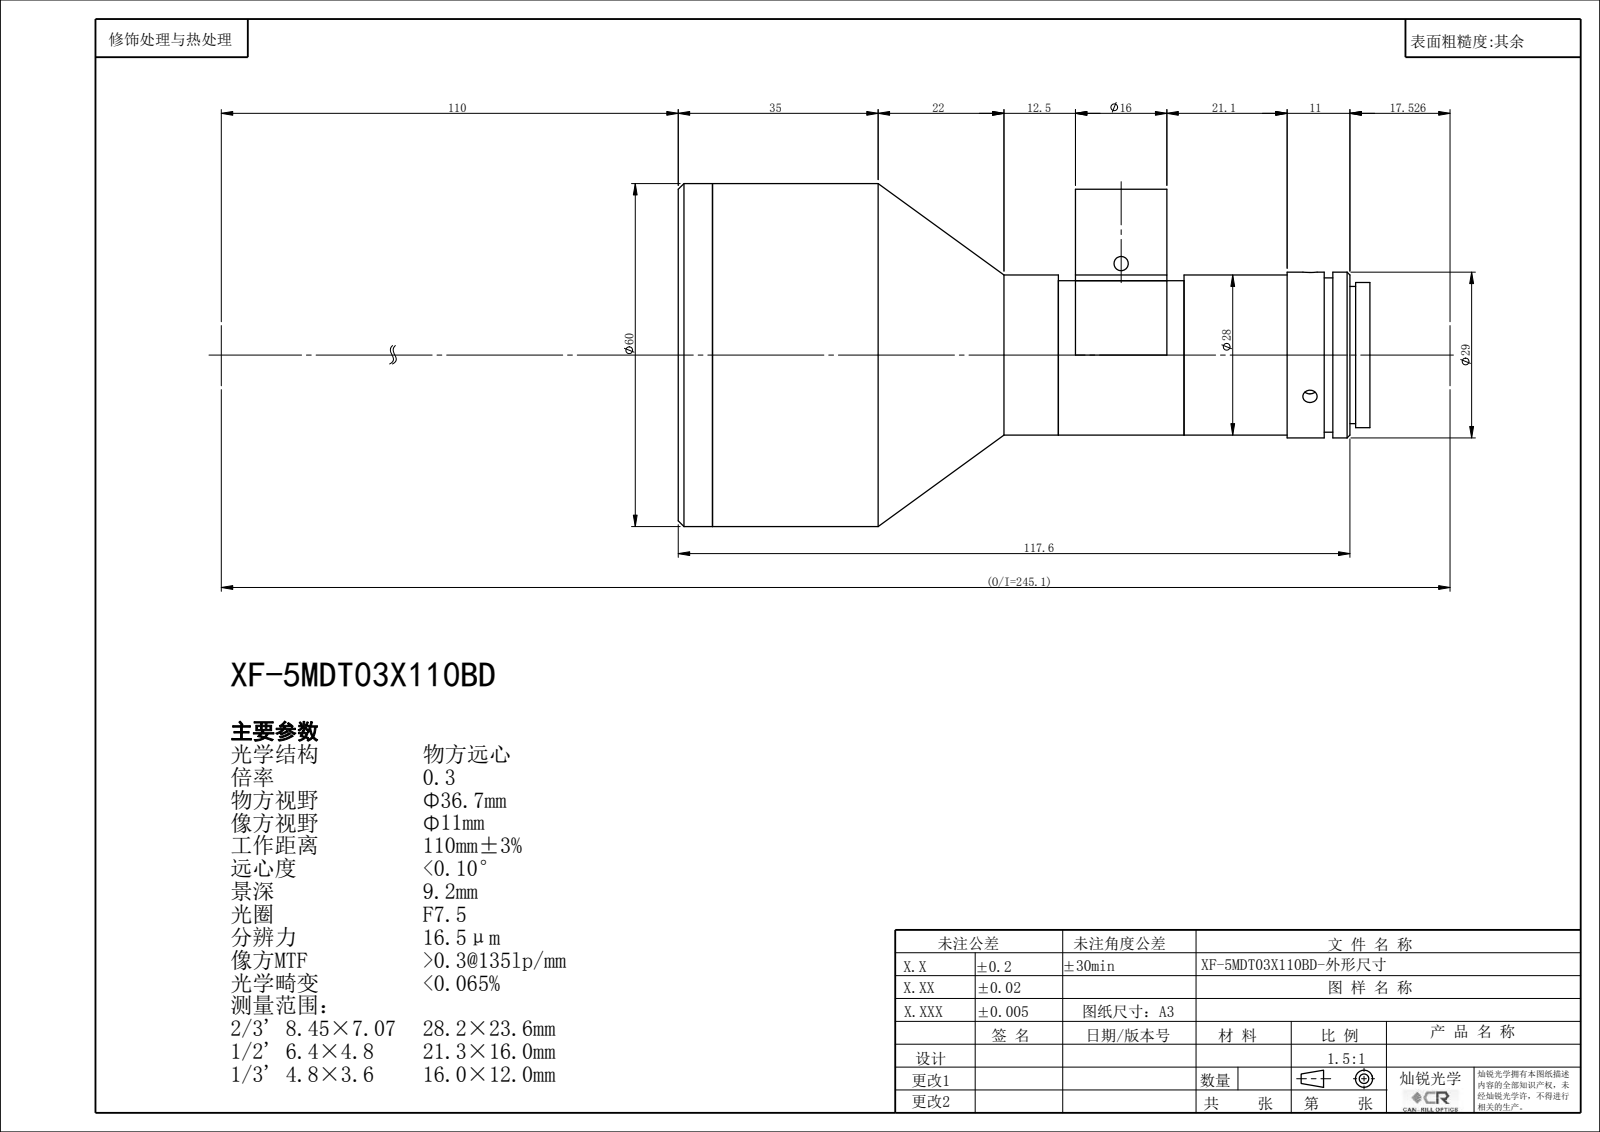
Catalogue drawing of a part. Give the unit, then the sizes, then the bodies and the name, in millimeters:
Units: millimetres
Overall size (bounding box): 121.09 × 60 × 60
Round holes (diameter × count): ⌀2.5 ×8, ⌀1.6 ×4, ⌀13 ×1, ⌀14 ×1, ⌀21.4 ×1, ⌀46 ×1, ⌀49.4 ×1, ⌀54 ×1
Round bosses / shafts (diameter × count): ⌀60 ×1, ⌀29 ×1, ⌀28 ×1, ⌀27 ×1, ⌀25.4 ×1, ⌀24 ×1, ⌀23 ×1, ⌀20 ×1
Main face-to-face distances: 6, 66.54, 60.54, 1, 49.05, 3, 2.38, 3.62, 64.16, 115.59
Hole centre spacings: 11.51, 13, 19, 23.02, 28.2, 40.67, 33.05
Bodies: 0 solids, 113 faces (36 planar, 69 cylindrical, 8 other)
STEP written by: SolidWorks 2014 (CONFIG_CONTROL_DESIGN)
